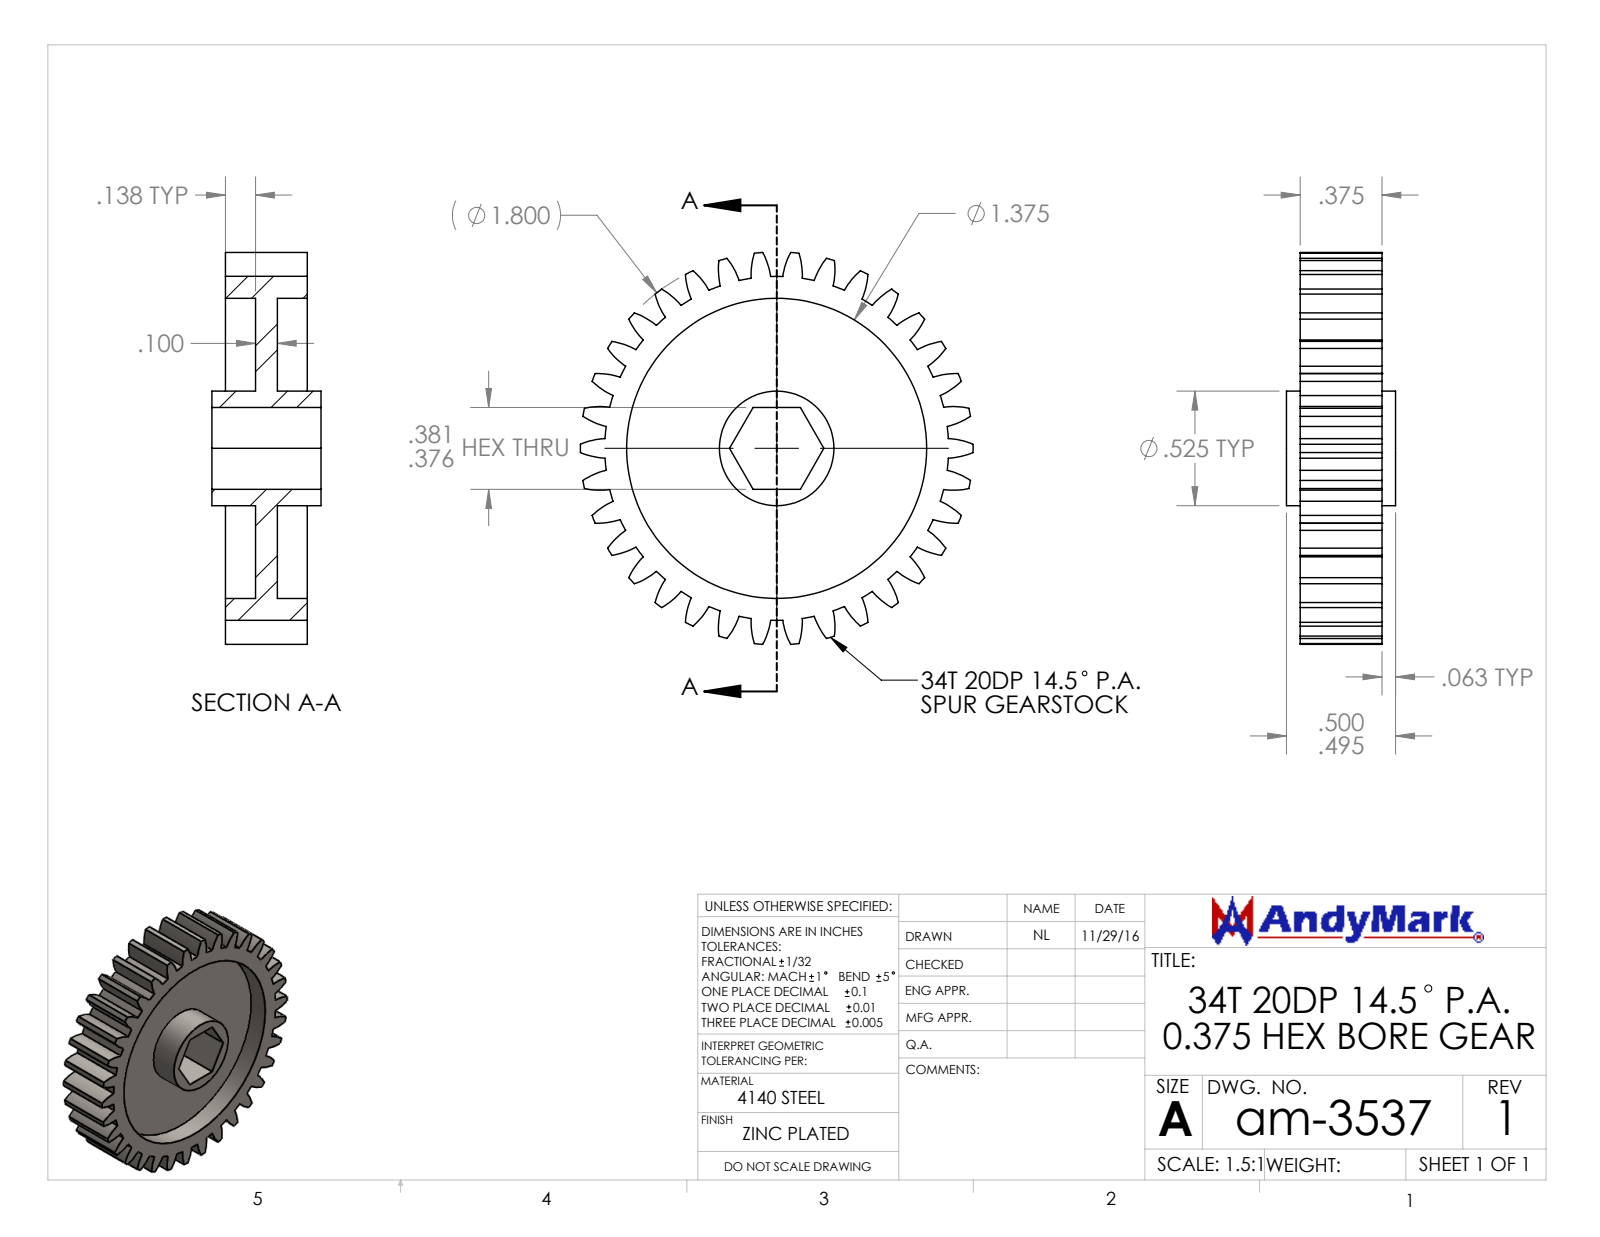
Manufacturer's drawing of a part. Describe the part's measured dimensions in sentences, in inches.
The part is named "am-3537 34T 20DP 375hex 375 FW". Its 3-D file was written by "SolidWorks 2014 (AUTOMOTIVE_DESIGN)". It is 1 solid with 161 faces: 12 planar, 149 cylindrical and 0 other. Overall it measures 1.8 by 1.795 by 0.5 inches. Its volume is 0.45 cubic inches and its surface area 10.86 square inches. Round holes: 1 of diameter 1.375. Round bosses or shafts: 1 of diameter 0.525. Partial cylindrical surfaces (rounded edges, fillets, slot ends): 68 of radius 0.34, 1 of radius 0.788, 1 of radius 0.9. The main face-to-face distances are 0.1, 0.238, 0.138, 0.137, 0.237, 0.375, 0.375, 0.2, 0.3, 0.063.
